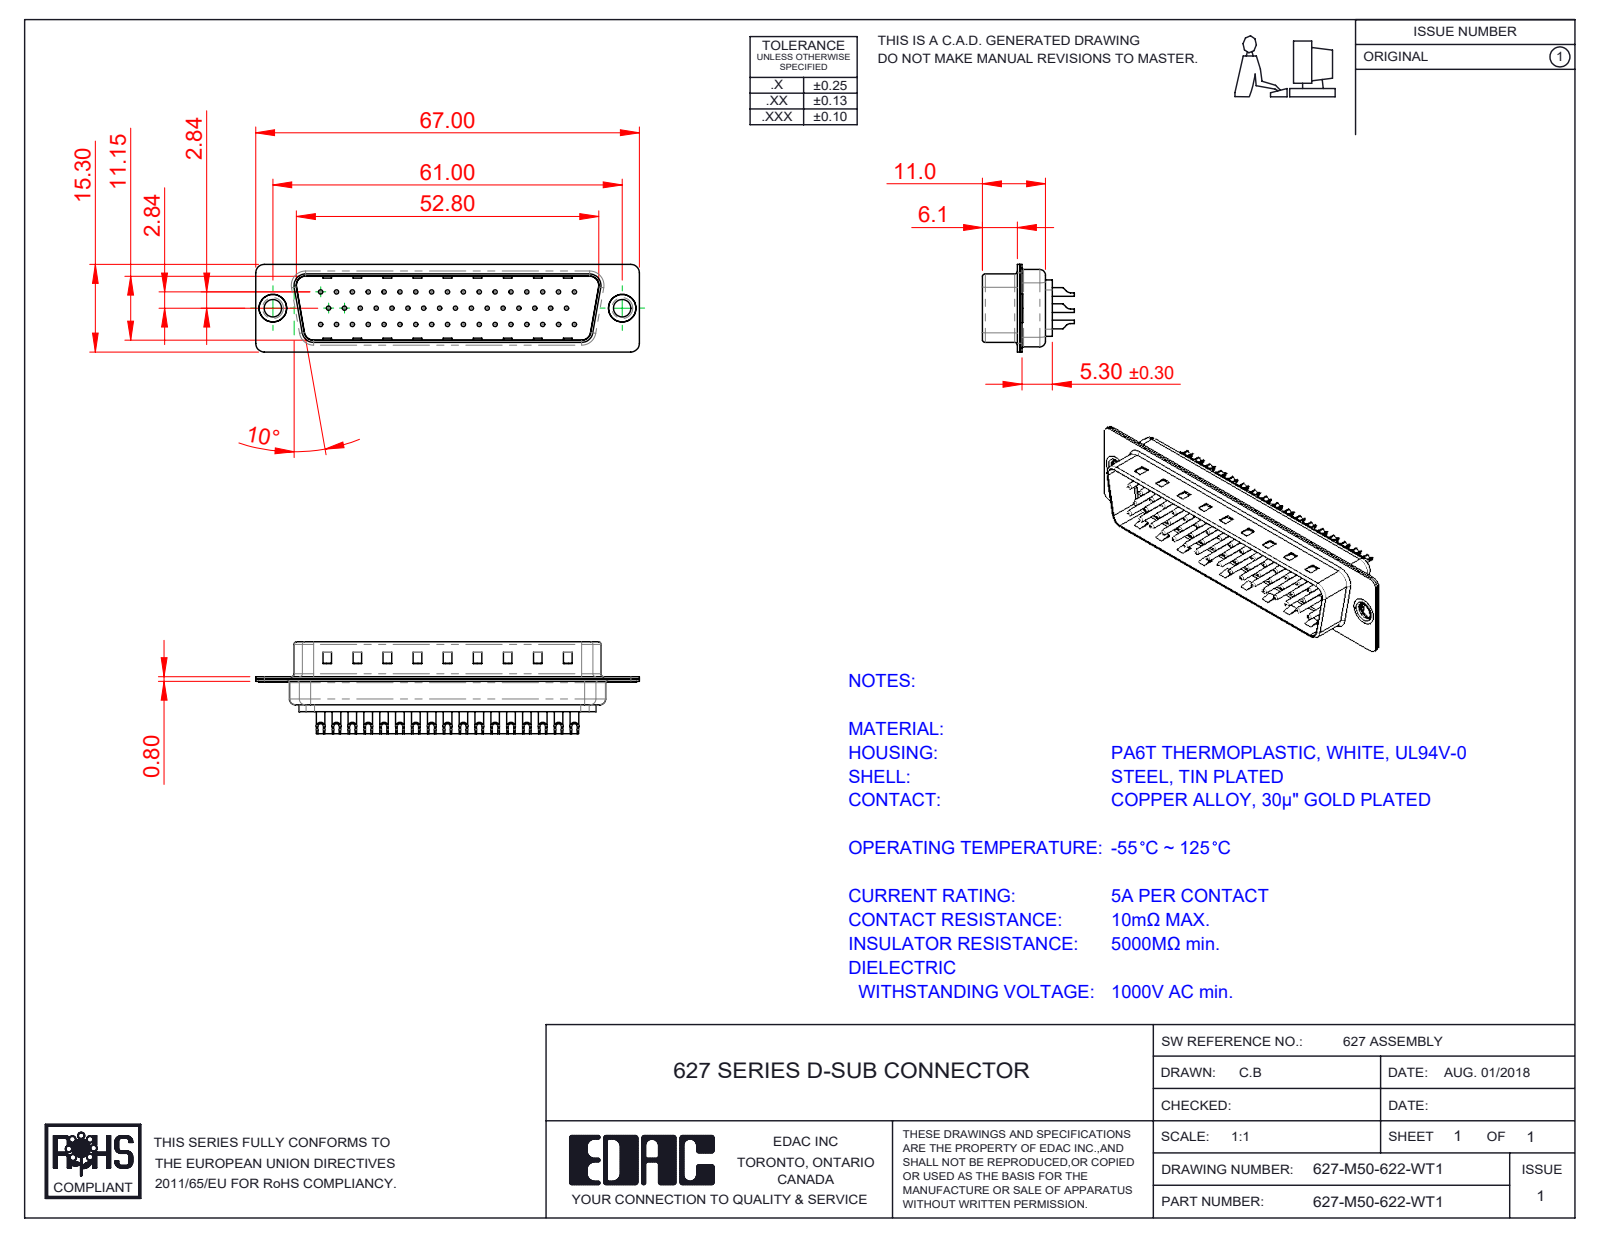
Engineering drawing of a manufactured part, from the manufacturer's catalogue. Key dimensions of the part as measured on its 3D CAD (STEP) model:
Part name (STEP PRODUCT): 627M Shell Rear_50 Contacts; 627M Shell Front_50 Contacts; 627M Thru Hole Rivet; 627-M50-622-WT1 (+4 more)
STEP written by: SolidWorks 2020 (CONFIG_CONTROL_DESIGN)
Units: millimetres
Bodies: 55 solids, 2236 faces (653 planar, 925 cylindrical, 658 other)
Overall size (bounding box): 67 × 16.05 × 15.3
Volume: 4 561 mm³ · Surface area: 11 022 mm²
Round holes (diameter × count): ⌀0.75 ×50, ⌀1 ×50, ⌀1.6 ×50, ⌀2 ×50, ⌀3.05 ×2, ⌀4 ×2, ⌀4.8 ×2
Round bosses / shafts (diameter × count): ⌀1.5 ×50, ⌀5 ×2, ⌀4.9 ×2, ⌀3.55 ×2
Partial cylindrical surfaces — rounded edges, fillets, slot ends (radius × count): R1.5 ×16, R2 ×12, R0.5 ×8, R1.6 ×8, R1 ×7, R0.25 ×4, R0.6 ×4, R0.65 ×4
Main face-to-face distances: 0.4, 11.55, 5.7, 6.1, 0.78, 0.77, 12.33, 12.32, 13.1, 5.3
Hole centre spacings: 3.16, 2.77, 5.54, 8.31, 11.08, 13.85, 16.62, 5.03
